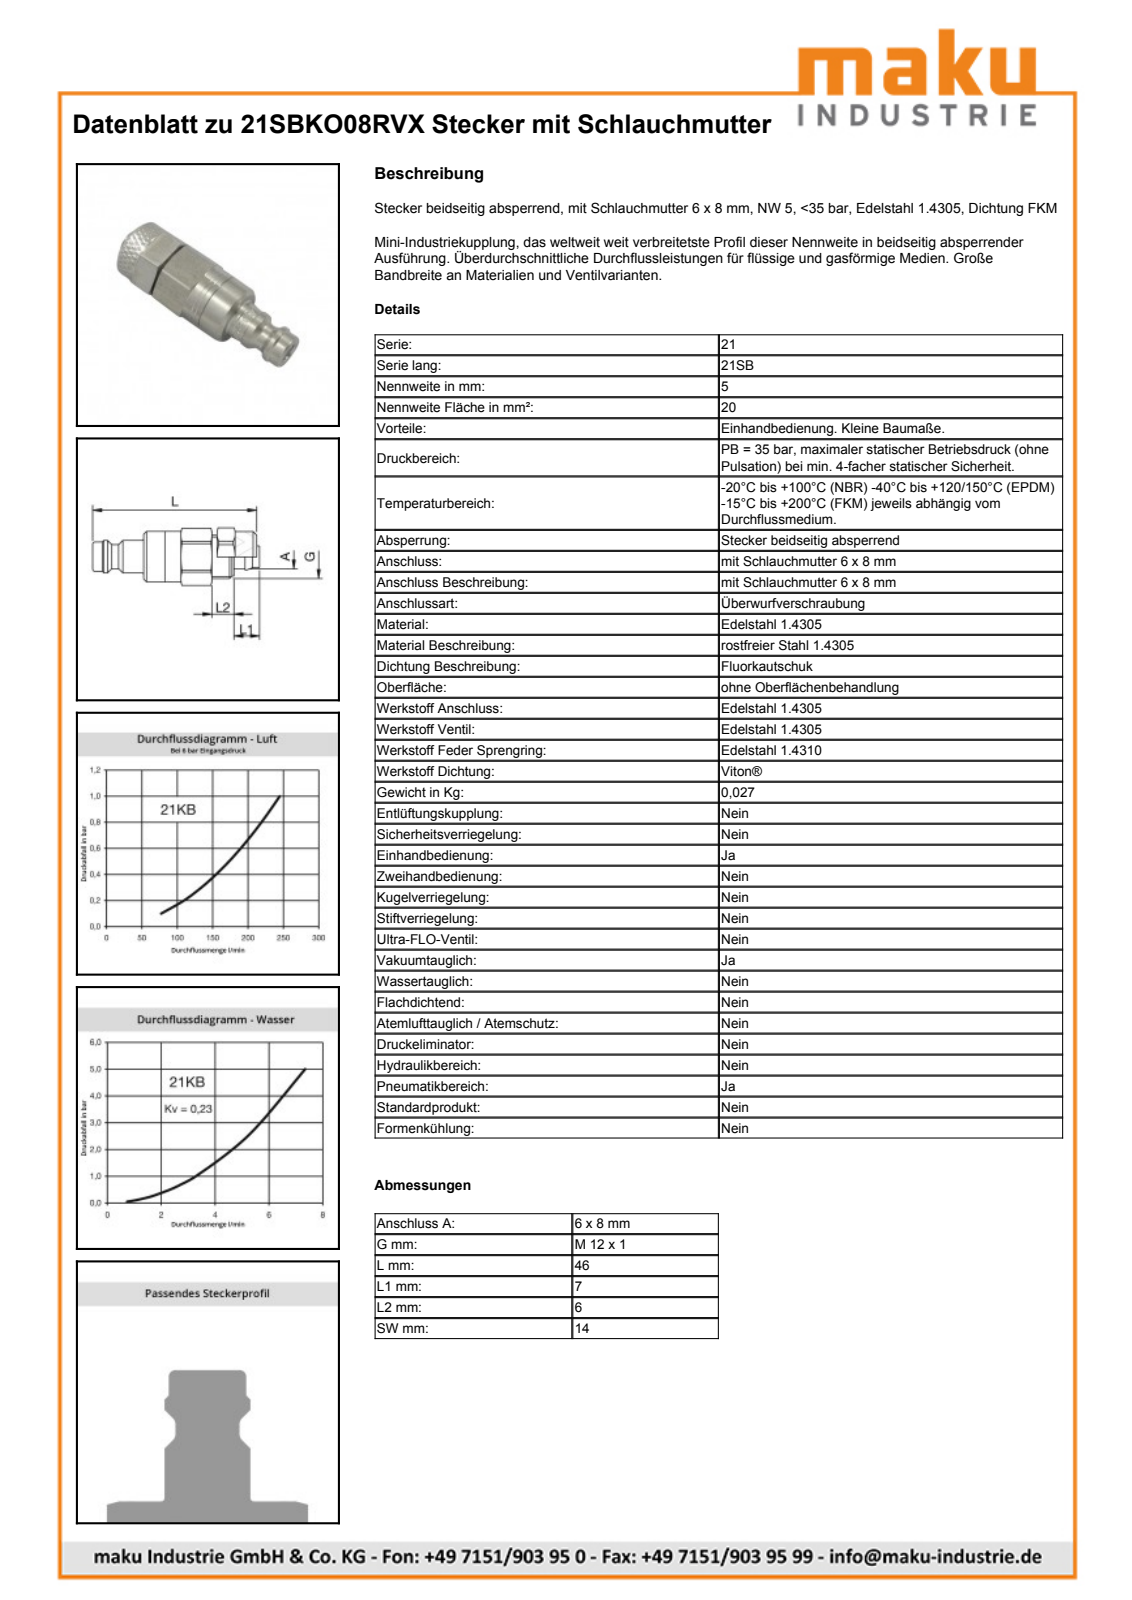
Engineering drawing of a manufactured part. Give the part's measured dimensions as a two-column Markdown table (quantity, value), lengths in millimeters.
| quantity | value |
| --- | --- |
| part name | D105924 |
| STEP written by | Autodesk Inventor 2011 (AUTOMOTIVE_DESIGN) |
| units | millimeters |
| bodies | 1 solid, 100 faces (23 planar, 29 cylindrical, 48 other) |
| overall size | 46 × 15.51 × 15.31 |
| volume | 5 174 mm³ |
| surface area | 3 002 mm² |
| round holes (diameter × count) | 11 × 1, 12 × 1, 12.1 × 1, 12.5 × 1, 12.6 × 1 |
| round bosses / shafts (diameter × count) | 14 × 1, 10.85 × 1, 10.79 × 1, 10.4 × 1, 9 × 1, 8.1 × 1, 6.7 × 1, 6.05 × 1 |
| partial cylindrical surfaces (radius × count) | 7.75 × 1, 7.9 × 1 |
| main face-to-face distances | 14, 12.1, 1.1, 5, 6.1, 13.9, 6, 18.7, 24.8, 30.8 |
